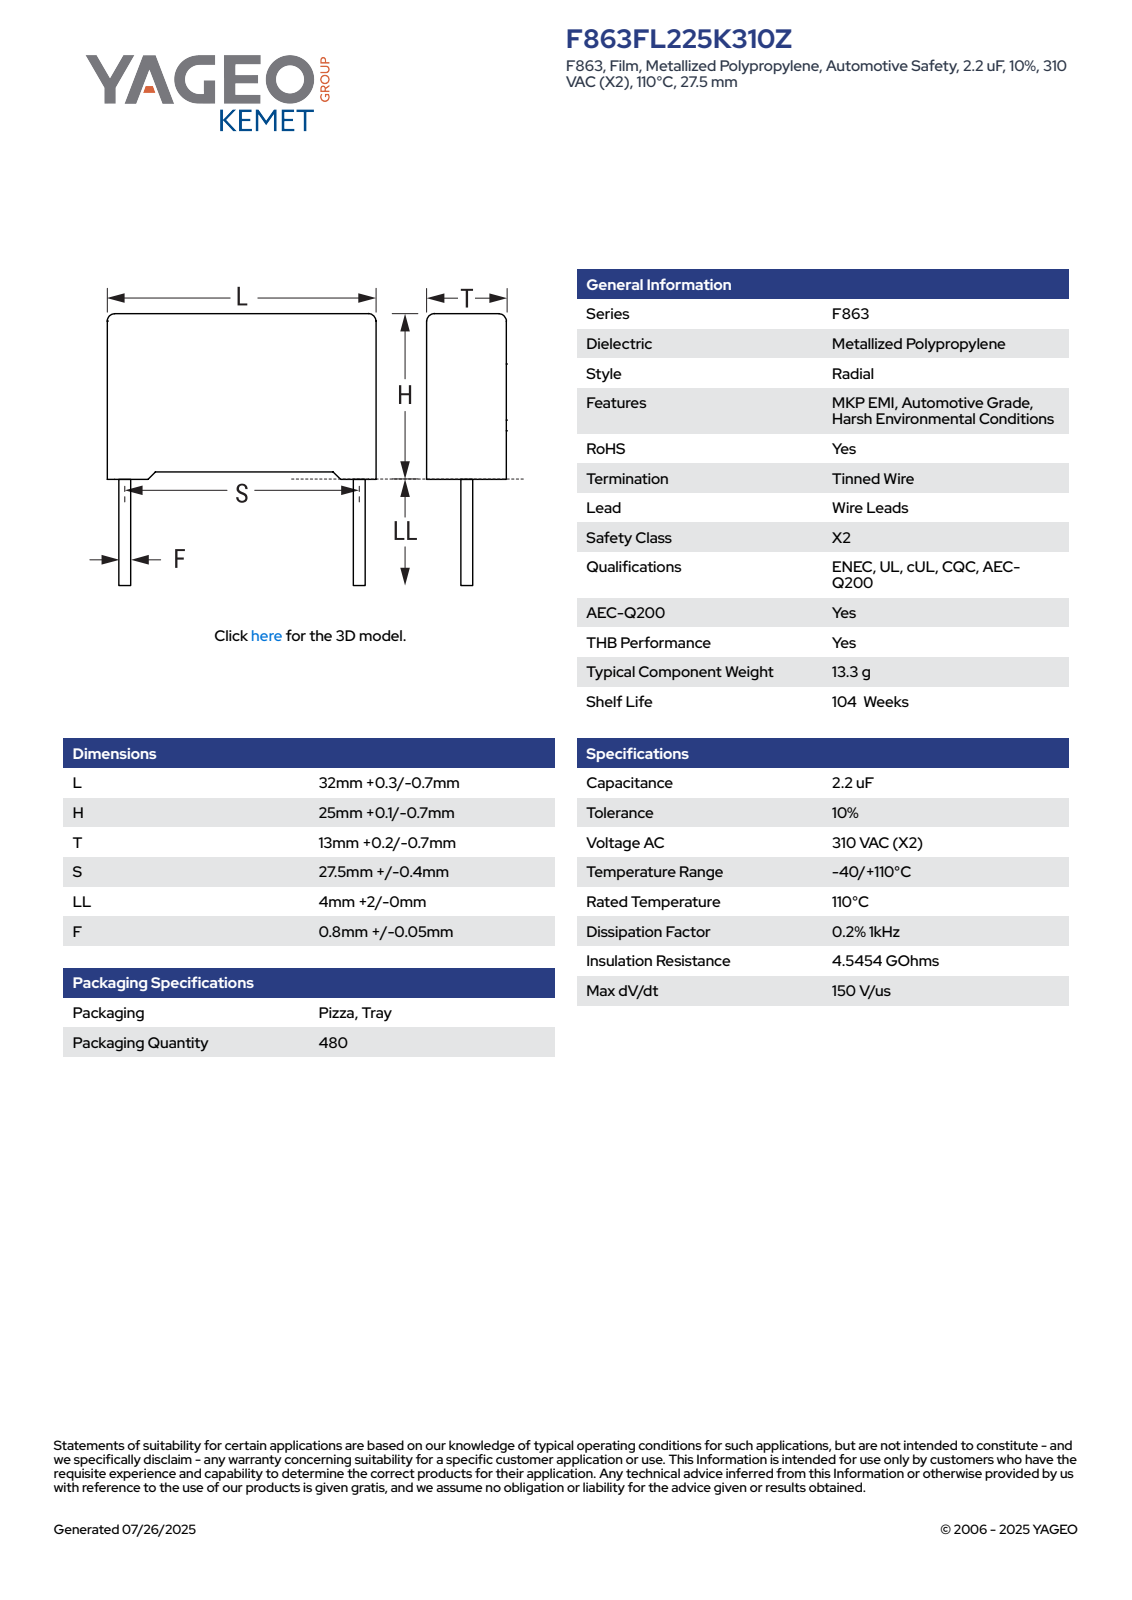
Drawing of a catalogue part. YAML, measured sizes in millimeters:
part_name: "CFR_RB_32X25X13_L32.3H25.1T13.2S27.5LL6F0.85"
step_written_by: "SolidWorks 2014 (AUTOMOTIVE_DESIGN)"
units: millimeters
bodies: {solids: 4, faces: 89, planar: 81, cylindrical: 8, other: 0}
overall_size: [32.3, 31.1, 13.21]
volume: 10224
surface_area: 3154
round_bosses_or_shafts:
  - {diameter: 0.85, count: 2}
partial_cylinders:
  - {radius: 0.9, count: 4}
face_to_face_distances: [13.2, 23.97, 32.3, 13.21, 0.6, 12.6, 0.61, 12, 12.61, 1.13]
